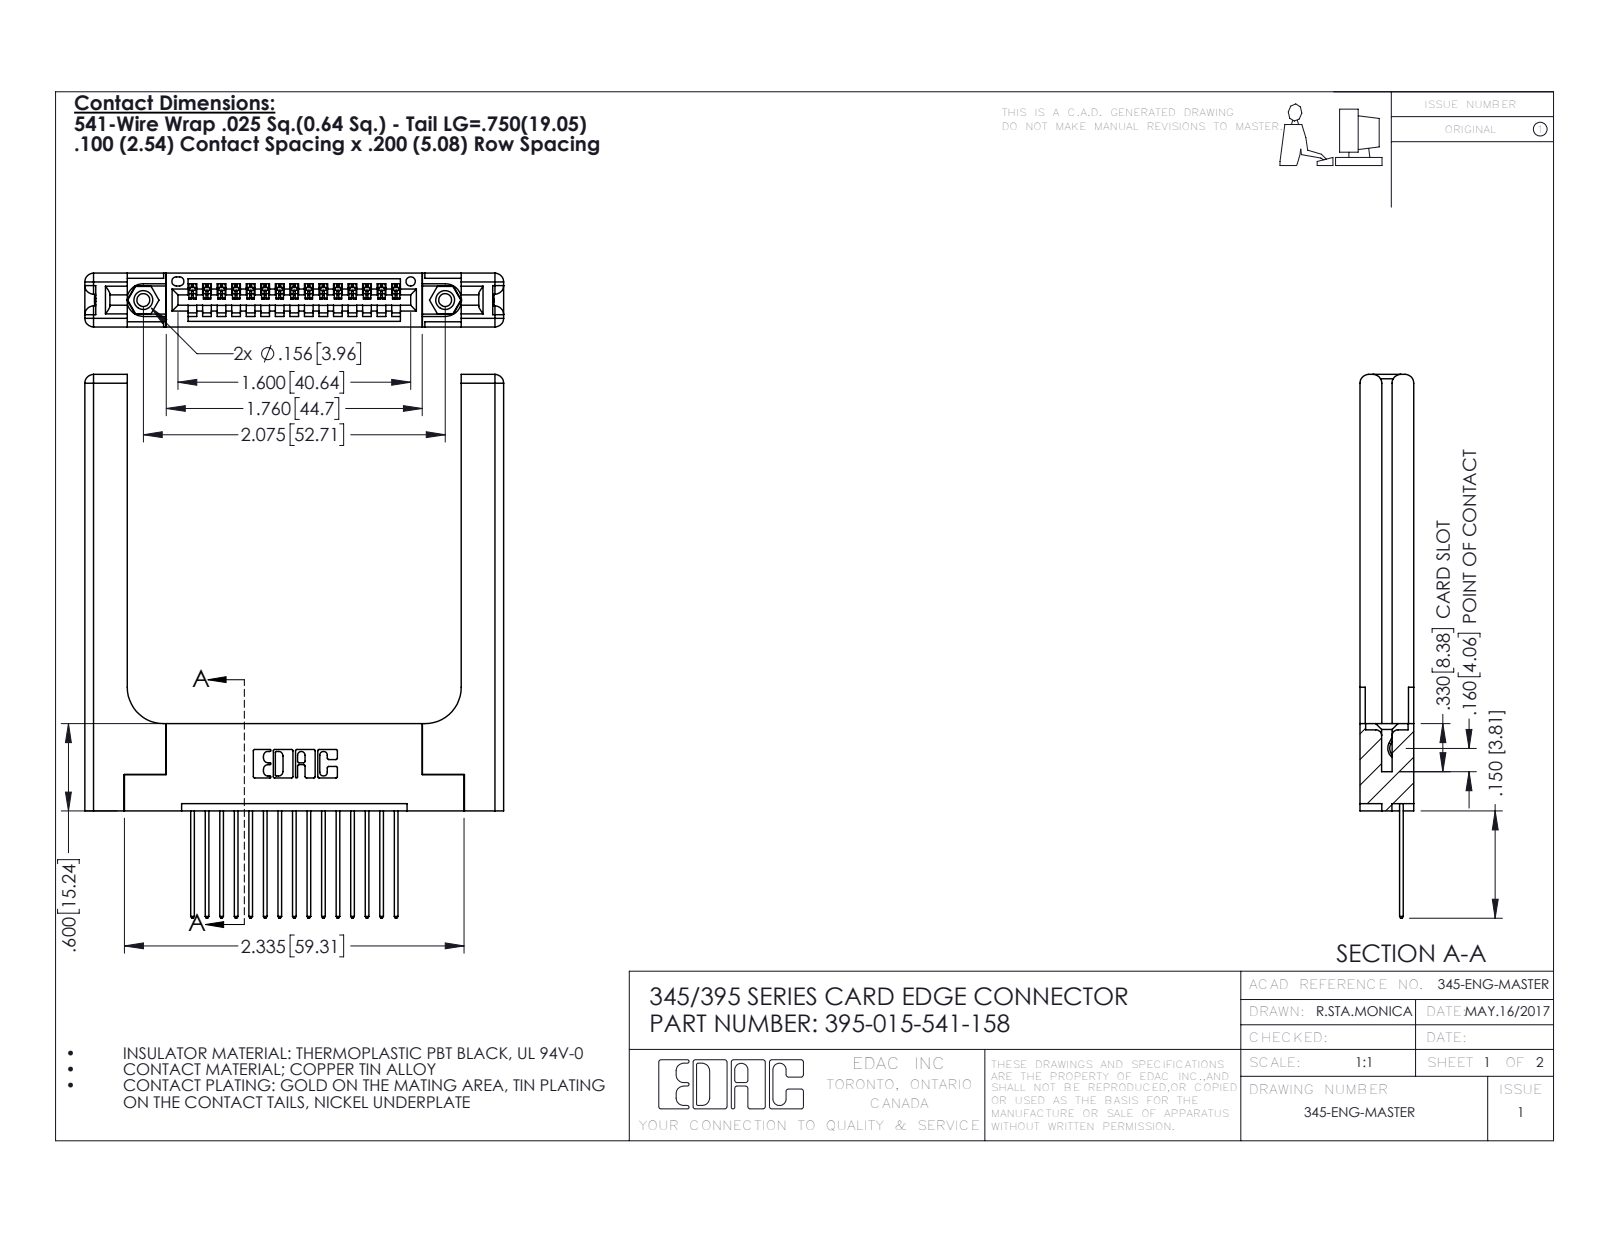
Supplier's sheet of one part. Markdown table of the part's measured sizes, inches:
| quantity | value |
| --- | --- |
| part name | 345-292-001_345-293-141; 345 Part_Flush Mounting Lugs - 0.156 Dia-TH; 395-015-541-158; 345-250-001_345-250-001-102 (+1 more) |
| STEP written by | SolidWorks 2016 (CONFIG_CONTROL_DESIGN) |
| units | inches |
| bodies | 20 solids, 1252 faces (828 planar, 364 cylindrical, 60 other) |
| overall size | 3.737 × 2.879 × 0.37 |
| volume | 0.932 in³ |
| surface area | 22.06 in² |
| round holes (diameter × count) | 0.089 × 2, 0.125 × 2, 0.156 × 2, 0.064 × 1 |
| round bosses / shafts (diameter × count) | 0.155 × 2 |
| partial cylindrical surfaces (radius × count) | 0.006 × 30, 0.01 × 30, 0.01 × 22, 0.06 × 16, 0.007 × 6, 0.031 × 6, 0.026 × 3, 0.03 × 2 |
| main face-to-face distances | 0.37, 0.072, 0.298, 0.15, 0.077, 0.148, 0.2, 0.22, 0.098, 0.272 |
| hole center spacings | 0.27, 1.842, 2.075 |
